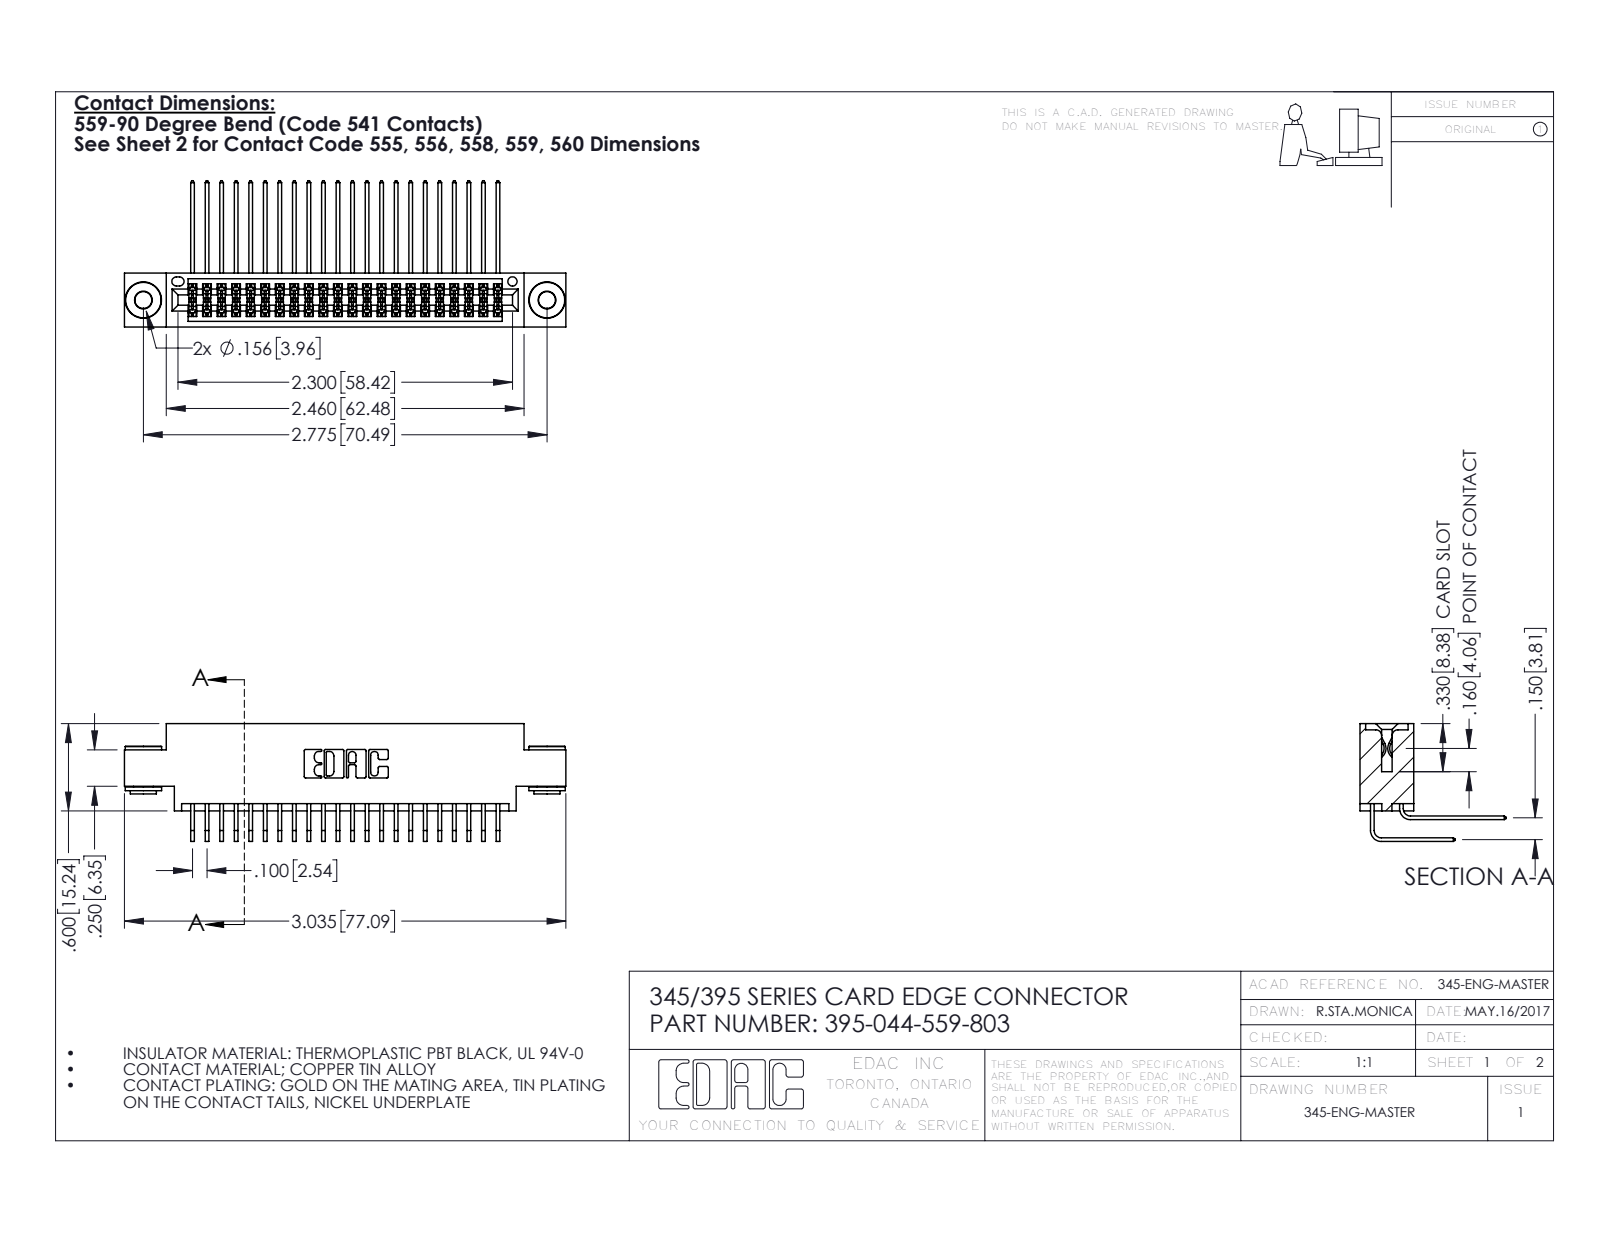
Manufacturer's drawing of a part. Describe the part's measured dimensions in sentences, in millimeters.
The part is named "345 Part_0.170 Offset - 0.156 Dia-TH; 395-044-559-803; 345-292-001_559 Tail - 2; 345-292-001_558 559 Tail - 1 (+1 more)". Its 3-D file was written by "SolidWorks 2016 (CONFIG_CONTROL_DESIGN)". It is 47 solids with 2456 faces: 1634 planar, 814 cylindrical and 8 other. Overall it measures 77.1 by 25.5 by 20.5 millimeters. Its volume is 7 460 cubic millimeters and its surface area 12 190 square millimeters. Round holes: 2 of diameter 2.9, 2 of diameter 4, 1 of diameter 1.6. Round bosses or shafts: 2 of diameter 6.4, 2 of diameter 4.6, 2 of diameter 3.5. Partial cylindrical surfaces (rounded edges, fillets, slot ends): 67 of radius 0.2, 22 of radius 0.3, 6 of radius 0.2, 6 of radius 0.8, 3 of radius 0.7, 2 of radius 0.4, 2 of radius 0.5, 2 of radius 0.6. The main face-to-face distances are 1.8, 7.6, 9.4, 5.1, 2.5, 6.9, 0.6, 4.4, 3.8, 5.7. The hole center spacings are 6.9, 64.5, 70.5.
